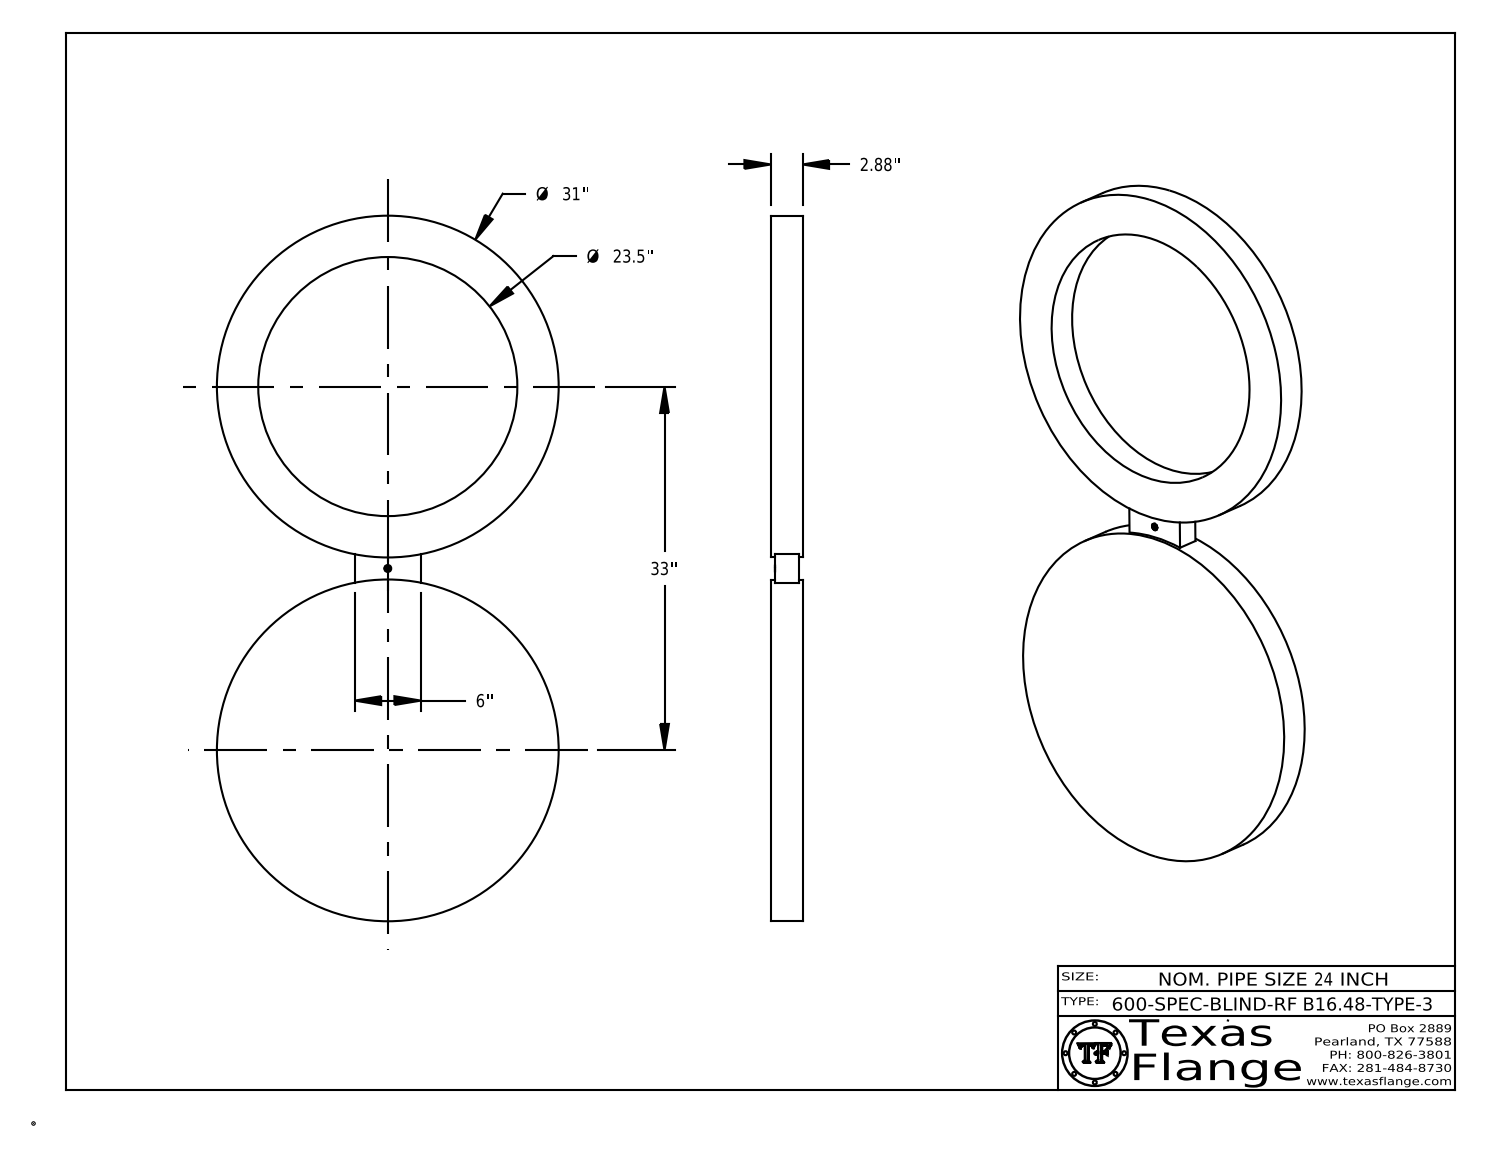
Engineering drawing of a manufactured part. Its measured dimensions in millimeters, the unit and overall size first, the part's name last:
Units: millimetres
Overall size (bounding box): 1625.6 × 787.4 × 73.2
Round holes (diameter × count): ⌀15.9 ×1, ⌀596.9 ×1
Round bosses / shafts (diameter × count): ⌀1 ×8, ⌀787.4 ×2, ⌀12.5 ×1
Main face-to-face distances: 73.2, 9.1, 64, 54.9, 152.4, 63.6, 54.5, 0.4, 9.5, 74.6
Hole centre spacings: 419.1
Volume: 51 240 000 mm³ · Surface area: 1 895 000 mm²
Bodies: 1 solid, 399 faces (373 planar, 26 cylindrical, 0 other)
Part name (STEP PRODUCT): 24-600-SPEC-BLIND-RF-B16.48-TYPE-3
STEP written by: CATIA V5 STEP AP214 (AUTOMOTIVE_DESIGN)
